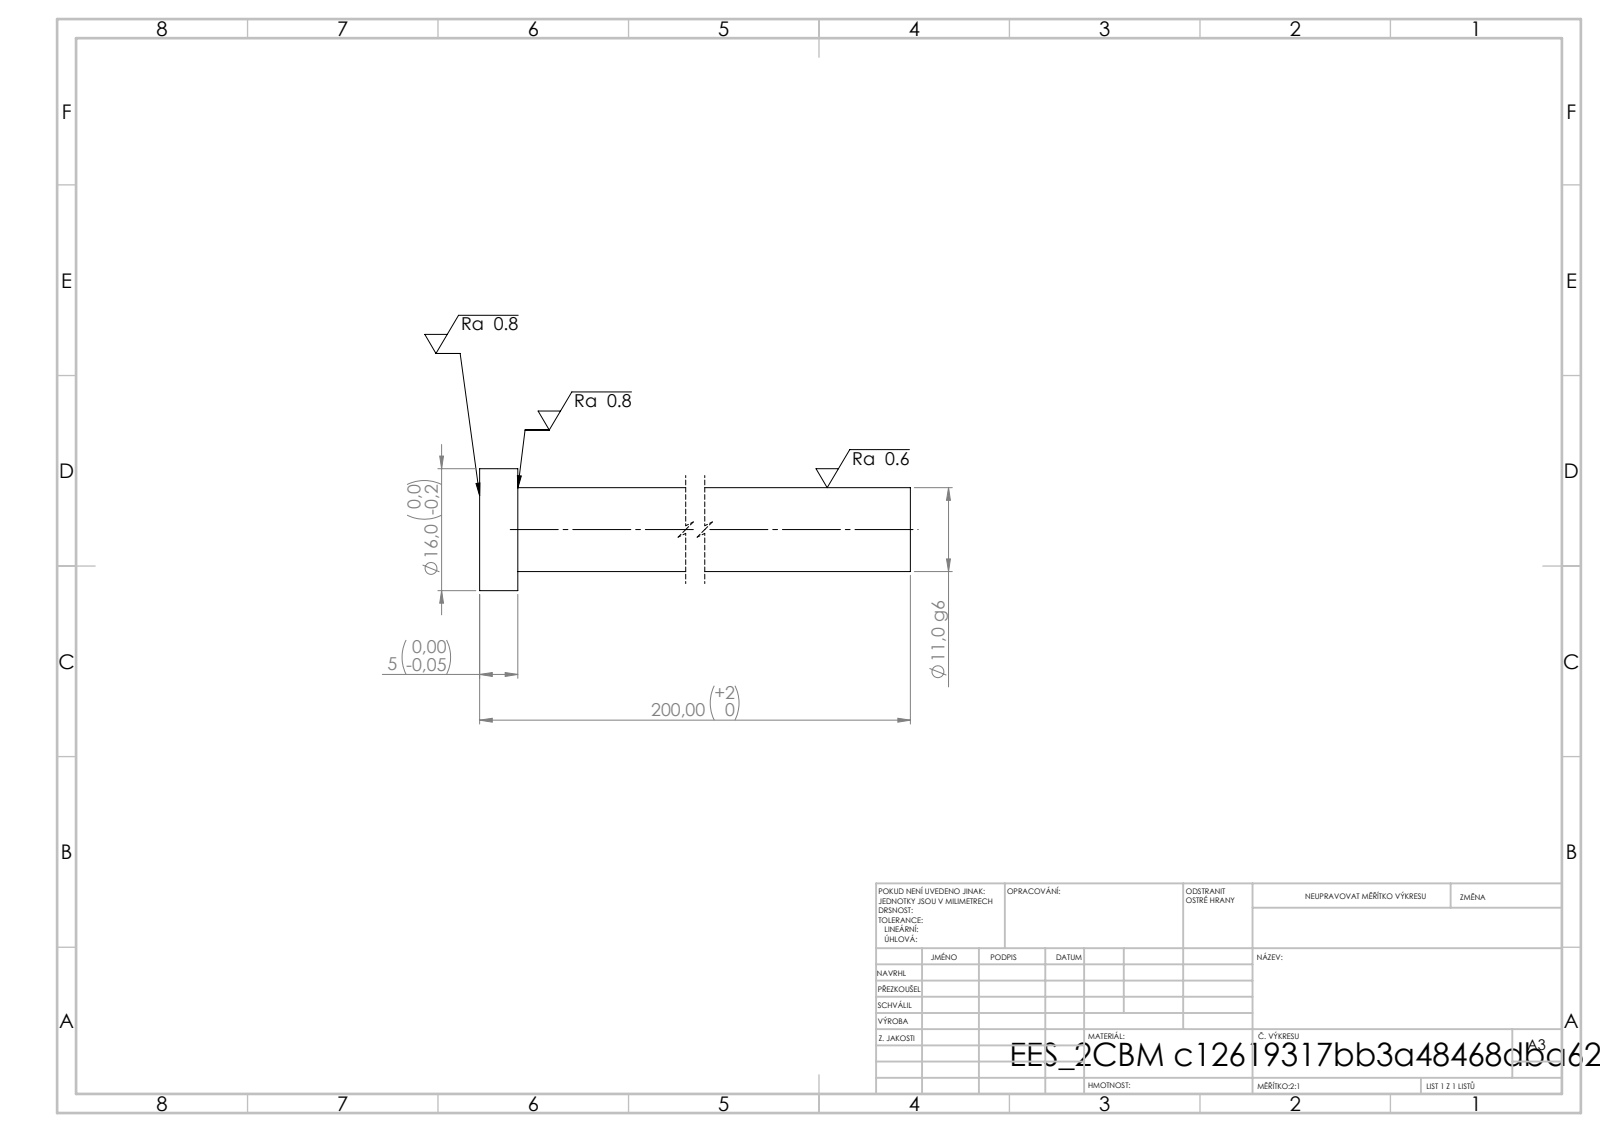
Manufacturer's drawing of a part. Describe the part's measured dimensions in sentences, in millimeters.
Its 3-D file was written by "SolidWorks 2019 (CONFIG_CONTROL_DESIGN)". It is 1 solid with 7 faces: 3 planar, 4 cylindrical and 0 other. Overall it measures 200 by 16 by 16 millimeters. Its volume is 19 537 cubic millimeters and its surface area 7 392 square millimeters. Round bosses or shafts: 1 of diameter 16, 1 of diameter 11. The main face-to-face distances are 5, 200, 195.
